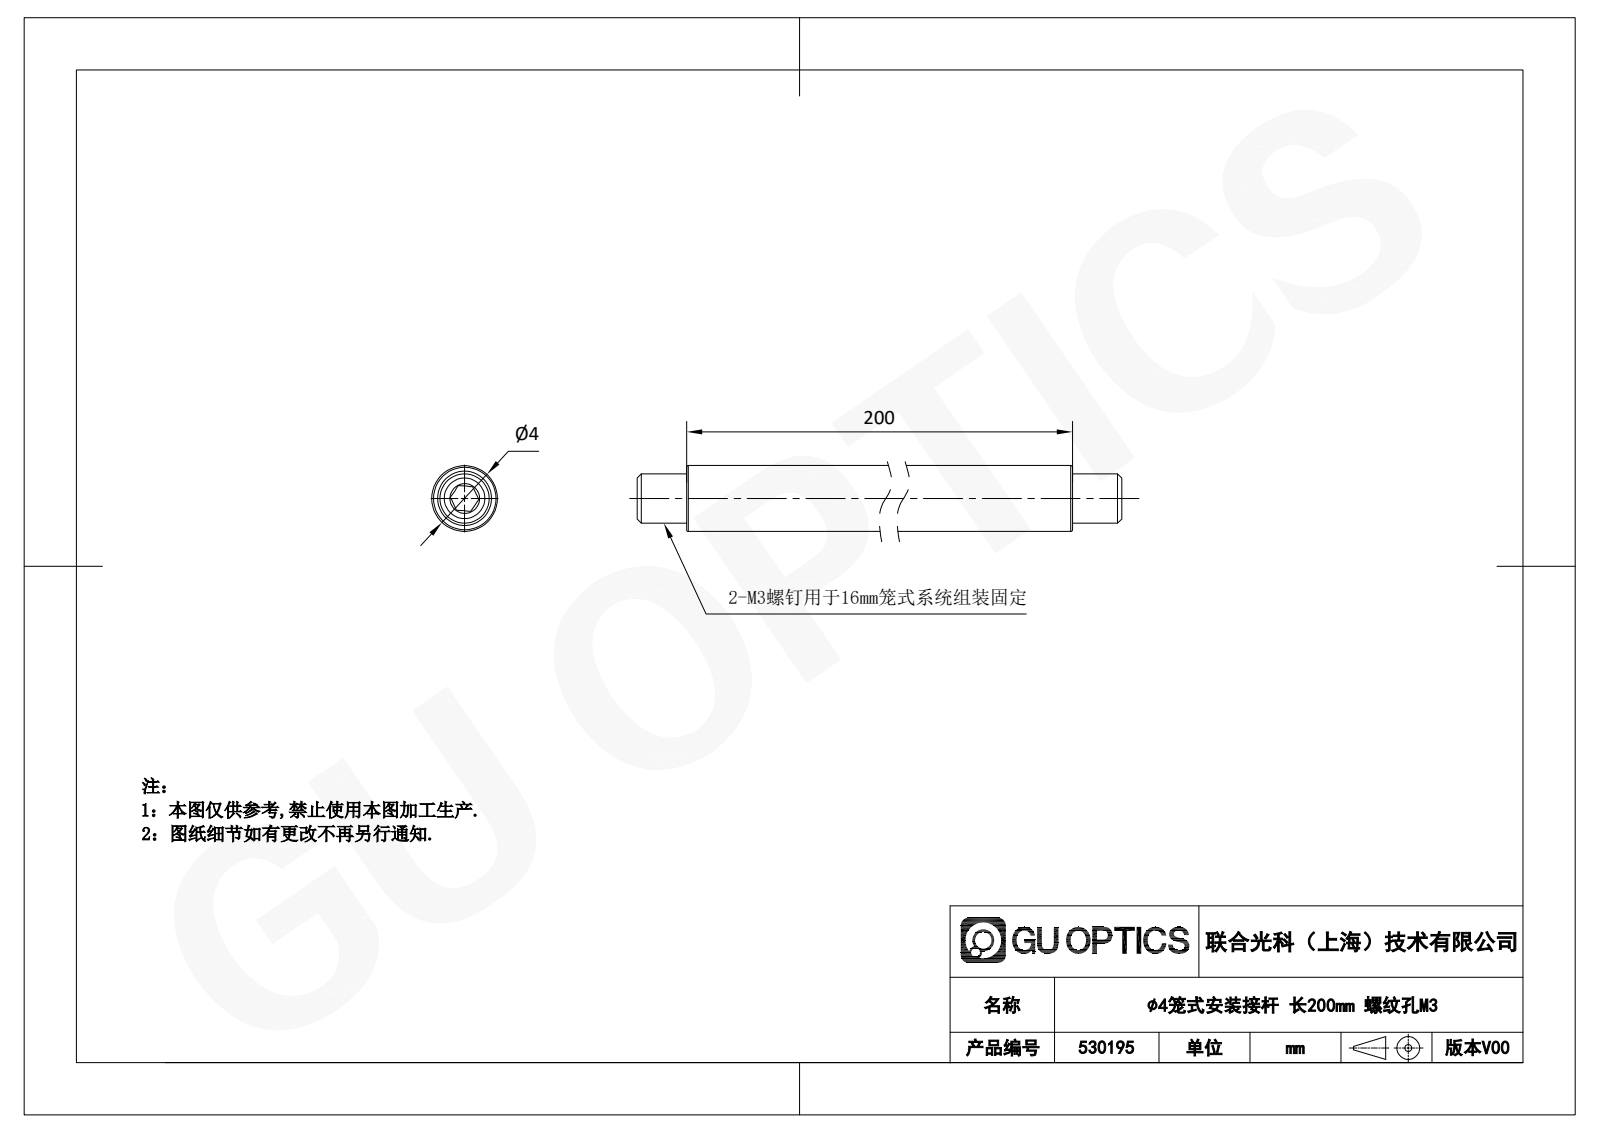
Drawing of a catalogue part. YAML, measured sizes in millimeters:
part_name: "530195"
step_written_by: "SolidWorks 2020 (CONFIG_CONTROL_DESIGN)"
units: millimeters
bodies: {solids: 3, faces: 37, planar: 20, cylindrical: 5, other: 12}
overall_size: [210, 4, 4]
volume: 2563
surface_area: 2803
round_holes:
  - {diameter: 2.5, count: 1}
round_bosses_or_shafts:
  - {diameter: 4, count: 1}
  - {diameter: 3, count: 1}
face_to_face_distances: [3, 197, 5, 8, 202, 205, 1.5, 200, 1, 209]
